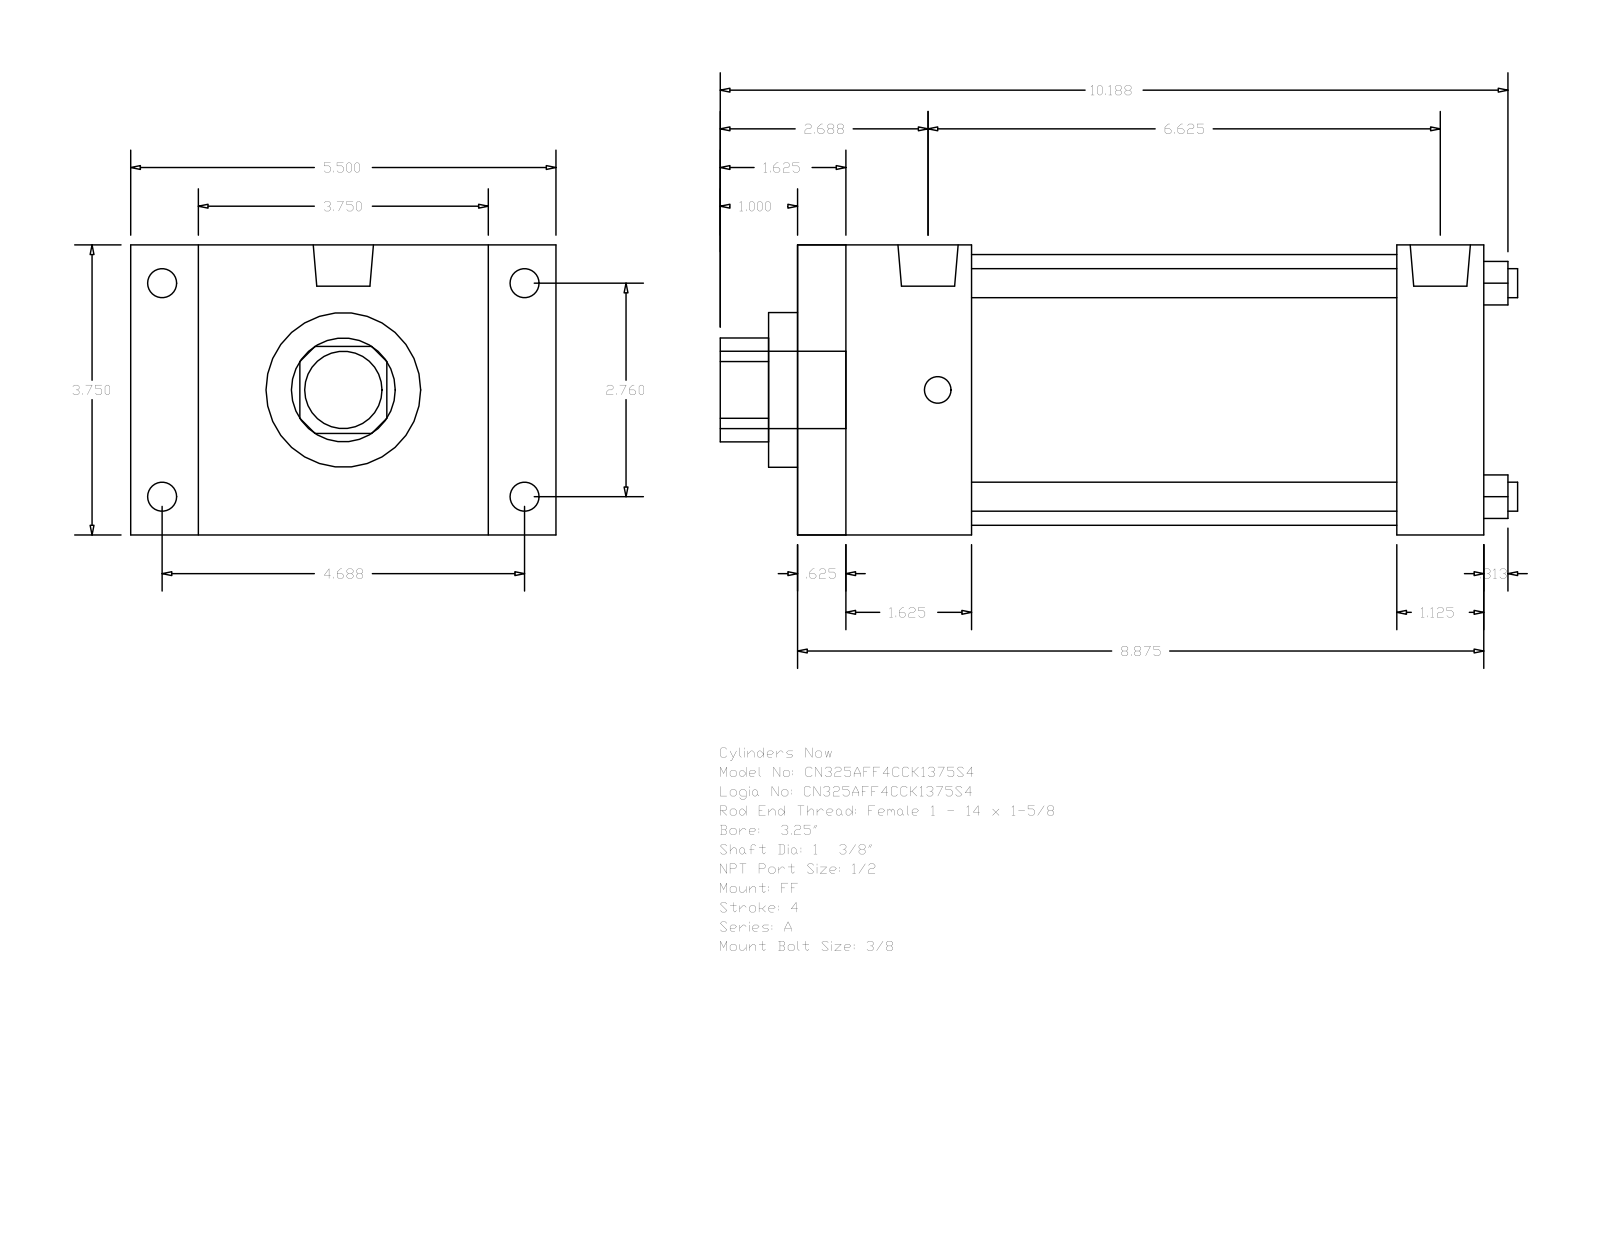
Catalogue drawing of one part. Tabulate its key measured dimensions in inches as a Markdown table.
| quantity | value |
| --- | --- |
| part name | A_FF__0325_1.375 |
| STEP written by | GSSL Pune (CONFIG_CONTROL_DESIGN) |
| units | inches |
| bodies | 0 solids, 92 faces (64 planar, 28 cylindrical, 0 other) |
| overall size | 10.313 × 5.5 × 3.75 |
| round holes (diameter × count) | 0.375 × 4, 1.375 × 1, 2 × 1, 3.5 × 1 |
| round bosses / shafts (diameter × count) | 0.375 × 4, 0.344 × 4, 0.778 × 2, 1 × 1 |
| partial cylindrical surfaces (radius × count) | 0.672 × 1 |
| main face-to-face distances | 3.75, 8.875, 8.25, 0.625, 5.5, 0.875, 4.625, 1.125, 2.25, 7.75 |
| hole center spacings | 1.952, 2.76, 3.903 |
